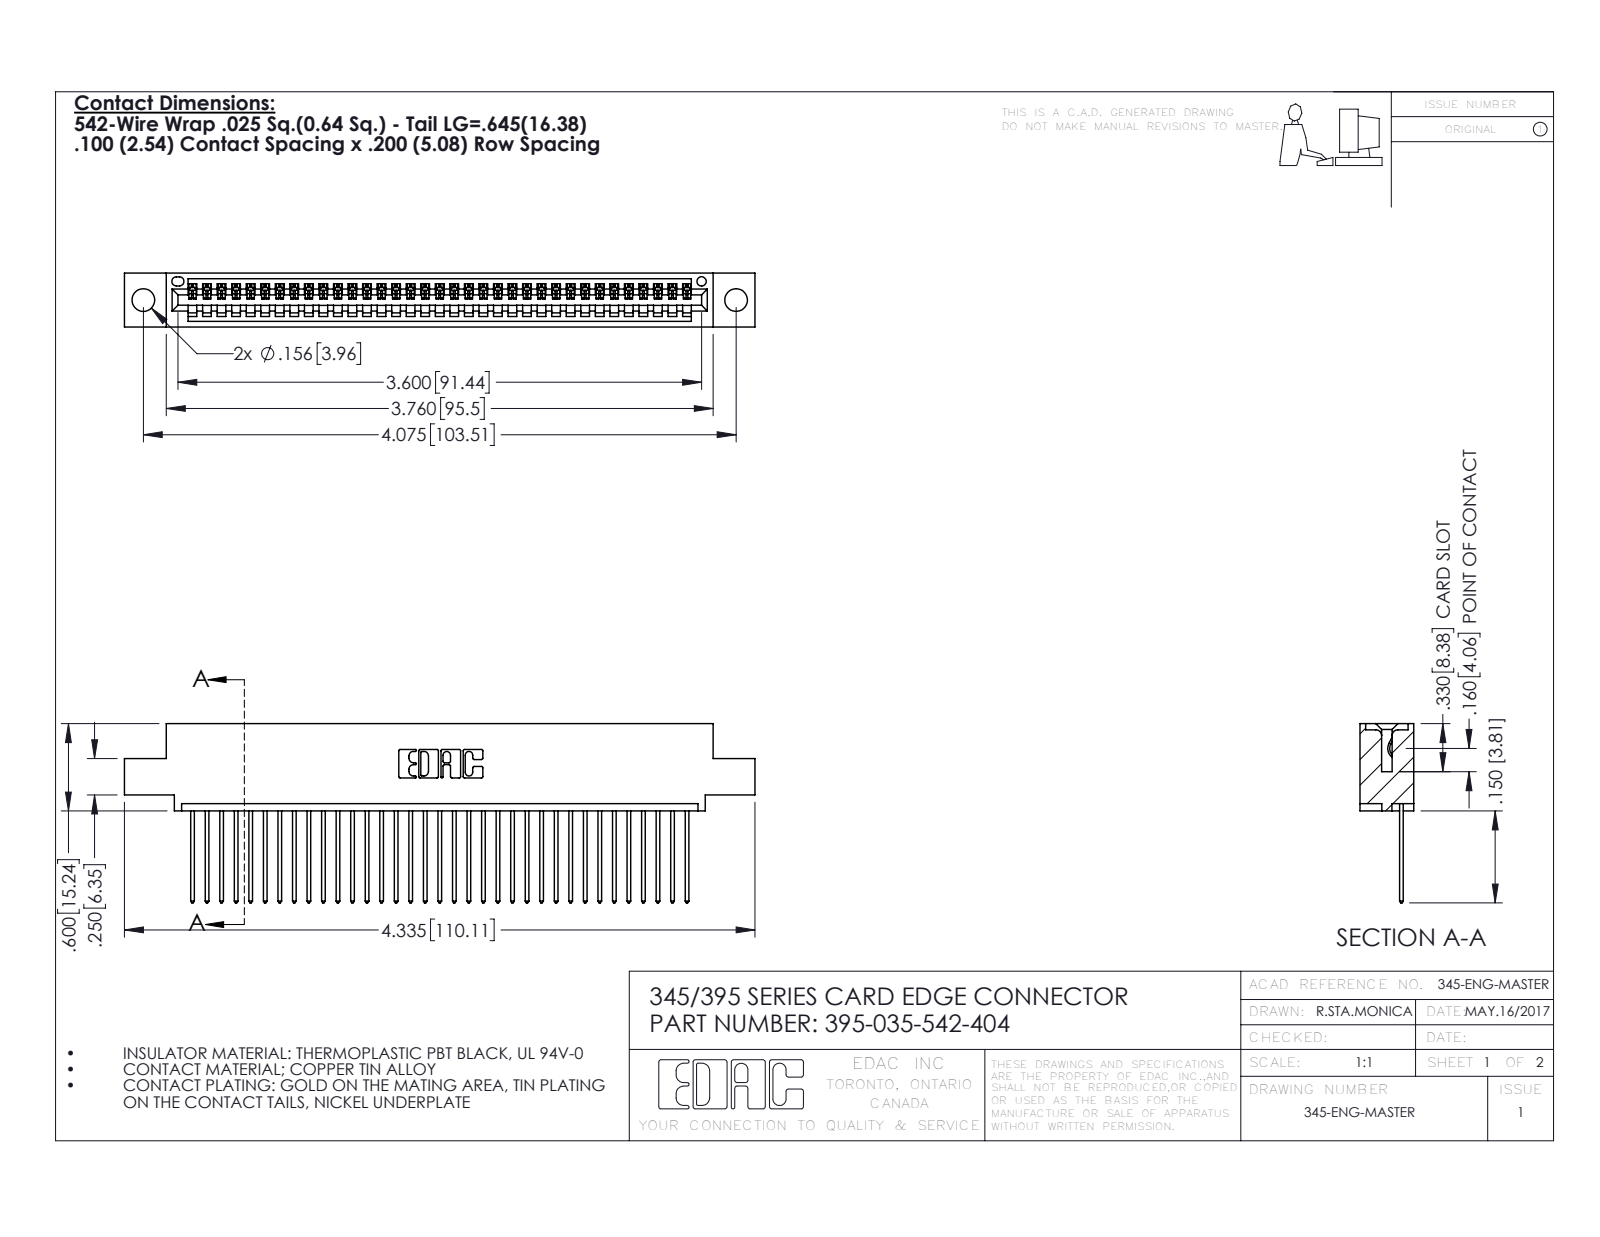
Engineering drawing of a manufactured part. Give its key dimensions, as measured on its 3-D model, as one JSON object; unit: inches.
{"part_name": "345 Part_0.110 Offset - 0.156 Dia-TH; 345-292-001_345-293-142; 395-035-542-404", "step_written_by": "SolidWorks 2016 (CONFIG_CONTROL_DESIGN)", "units": "inches", "bodies": {"solids": 36, "faces": 2160, "planar": 1484, "cylindrical": 676, "other": 0}, "overall_size": [4.335, 1.232, 0.37], "volume_in3": 0.63, "surface_area_in2": 21.7, "round_holes": [[0.156, 2], [0.064, 1]], "partial_cylinders_radius": [[0.006, 70], [0.01, 70], [0.01, 22], [0.007, 6], [0.031, 6], [0.026, 3], [0.031, 2], [0.04, 2]], "face_to_face_distances": [0.298, 0.072, 0.37, 0.098, 0.272, 0.025, 0.2, 0.225, 0.149, 0.072], "hole_center_spacings": [0.27, 3.839, 4.075]}
